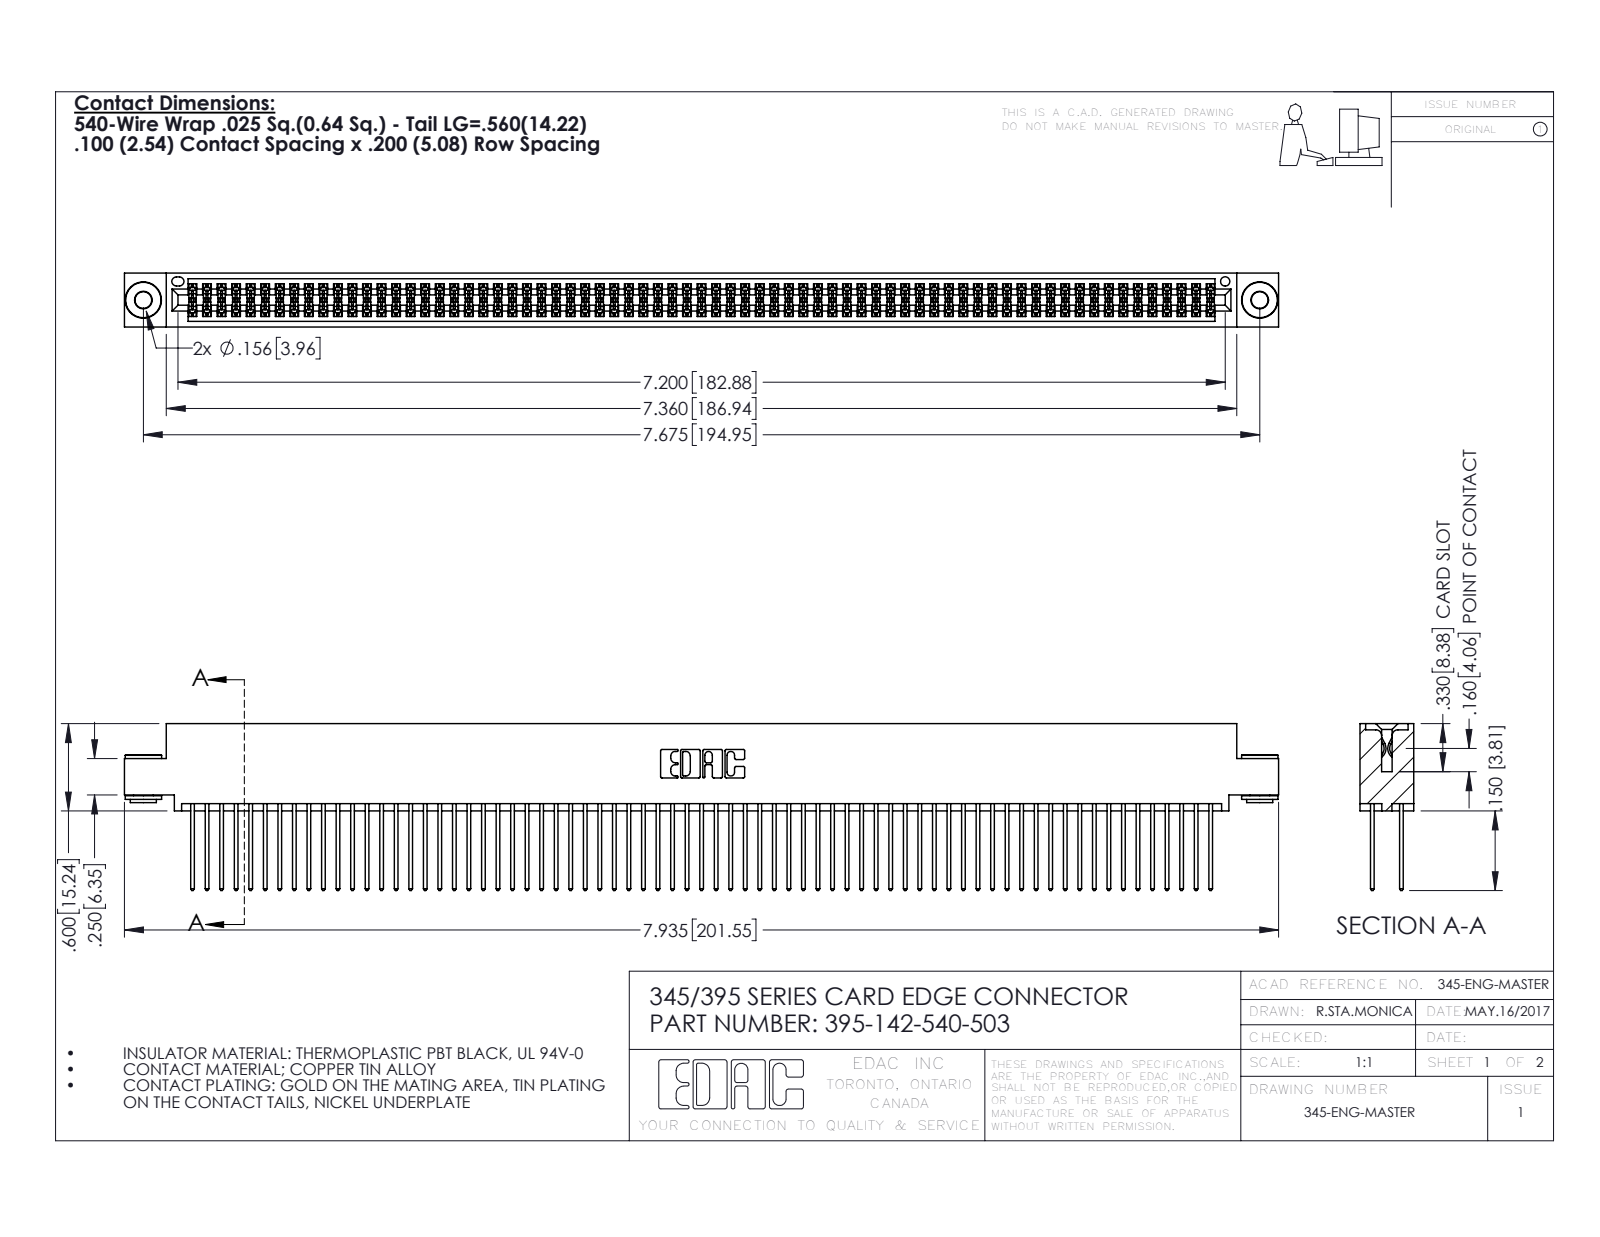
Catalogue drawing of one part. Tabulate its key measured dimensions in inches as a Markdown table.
| quantity | value |
| --- | --- |
| part name | 395-142-540-503; 345 Part_0.110 Offset - 0.156 Dia-TH; 345-292-001_345-293-140; 345-250-002_345-250-002-102 |
| STEP written by | SolidWorks 2016 (CONFIG_CONTROL_DESIGN) |
| units | inches |
| bodies | 145 solids, 7268 faces (4780 planar, 2480 cylindrical, 8 other) |
| overall size | 7.935 × 1.147 × 0.37 |
| volume | 1.241 in³ |
| surface area | 51.79 in² |
| round holes (diameter × count) | 0.116 × 2, 0.156 × 2, 0.064 × 1 |
| round bosses / shafts (diameter × count) | 0.25 × 2, 0.18 × 2, 0.136 × 2 |
| partial cylindrical surfaces (radius × count) | 0.006 × 213, 0.01 × 142, 0.01 × 22, 0.007 × 6, 0.031 × 6, 0.026 × 3, 0.014 × 2, 0.019 × 2 |
| main face-to-face distances | 0.072, 0.298, 0.2, 0.025, 0.098, 0.272, 0.225, 0.37, 0.175, 0.149 |
| hole center spacings | 0.27, 7.439, 7.675 |
